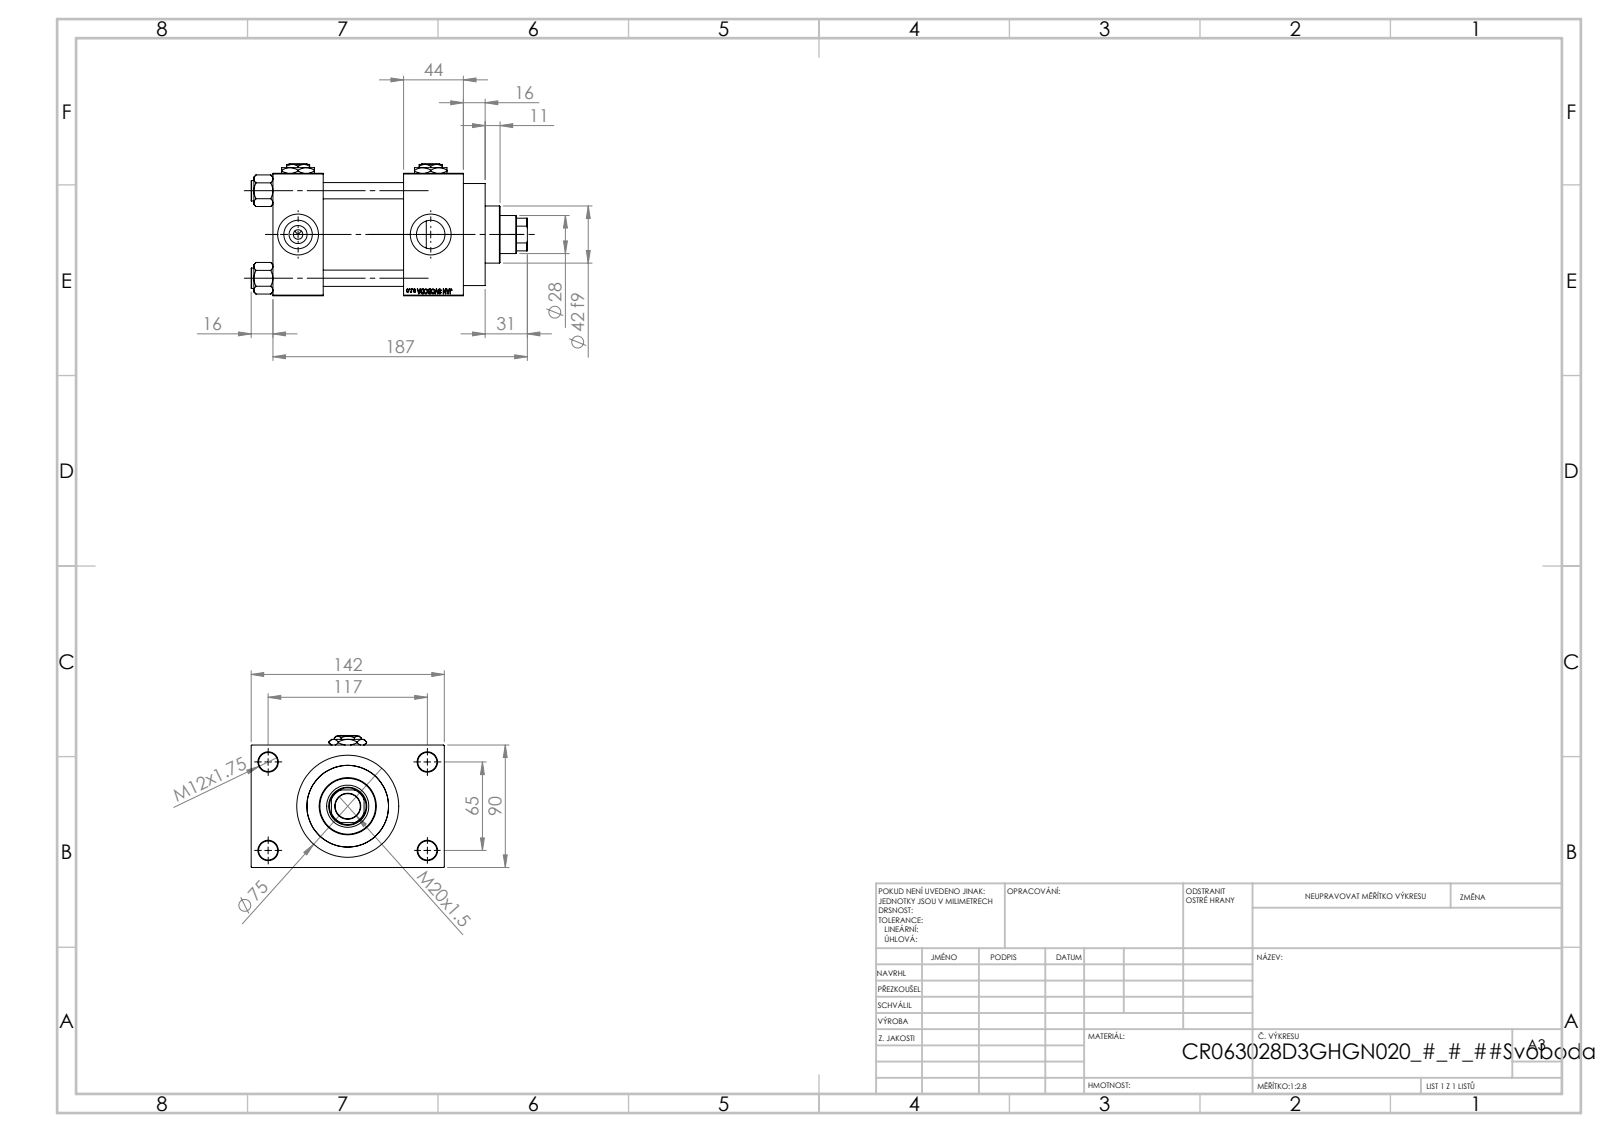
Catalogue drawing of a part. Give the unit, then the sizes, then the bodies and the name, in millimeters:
Units: millimetres
Overall size (bounding box): 203 × 142 × 97
Round holes (diameter × count): ⌀12 ×4, ⌀14 ×4, ⌀20.96 ×4, ⌀30 ×4, ⌀7 ×3, ⌀18.5 ×1, ⌀28 ×1, ⌀31 ×1, ⌀50 ×1, ⌀60 ×1, ⌀63 ×1
Round bosses / shafts (diameter × count): ⌀15 ×4, ⌀75 ×1, ⌀69 ×1, ⌀42 ×1
Partial cylindrical surfaces — rounded edges, fillets, slot ends (radius × count): R13.5 ×1
Main face-to-face distances: 90, 59, 37, 96, 140, 103, 44, 26, 116, 16
Hole centre spacings: 26.35, 45.47, 64.3, 66.92, 69.81, 90.65, 111.34, 65
Volume: 1 091 000 mm³ · Surface area: 204 942 mm²
Bodies: 13 solids, 1204 faces (545 planar, 99 cylindrical, 560 other)
Part name (STEP PRODUCT): V215_VC_A; NUT_M5_D; V215CR_D_Body; V215CR_VCP_D (+2 more)
STEP written by: SolidWorks 2019 (CONFIG_CONTROL_DESIGN)
